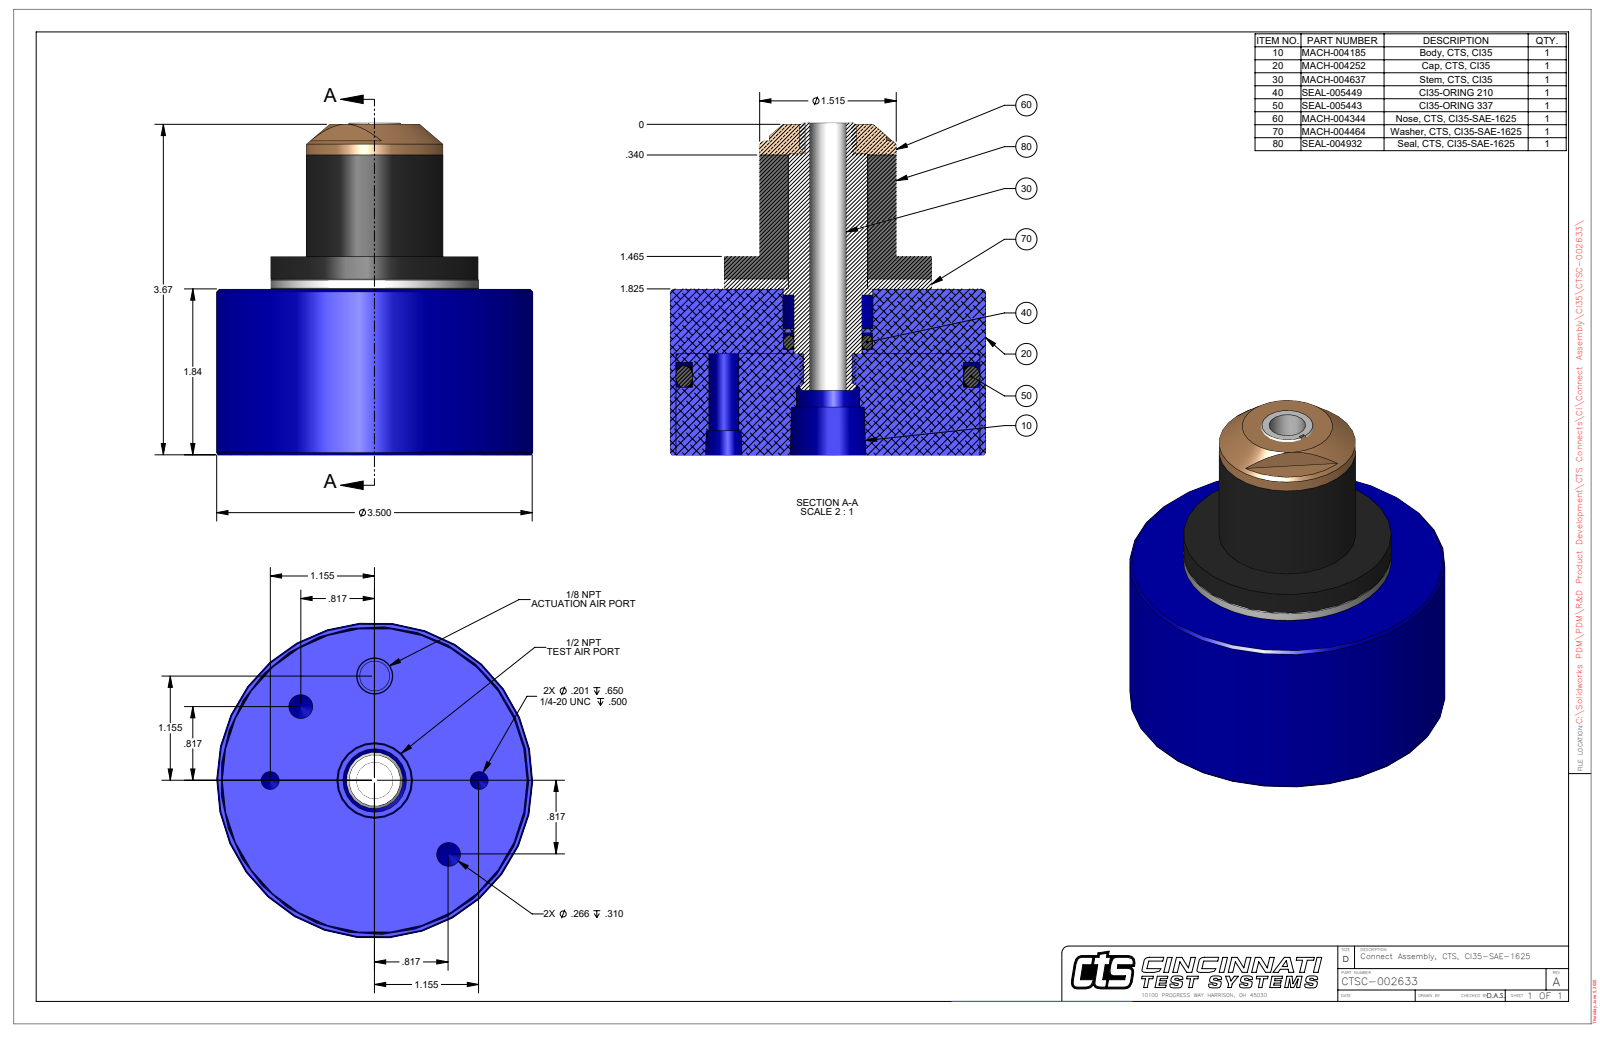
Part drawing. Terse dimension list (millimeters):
name: CTSC-002633
written by: SolidWorks 2023 (AUTOMOTIVE_DESIGN)
unit: mm
bodies: 1 solid, 74 faces (20 planar, 27 cylindrical, 27 other)
size: 93.5 × 88.9 × 88.9
volume: 340 400 mm³; area: 45 740 mm²
holes: 2× ⌀5.1, 2× ⌀6.8, 1× ⌀8.4, 1× ⌀10.3, 1× ⌀17.9, 1× ⌀85.7
bosses: 1× ⌀88.9, 1× ⌀85.5, 1× ⌀58.4, 1× ⌀38.5
rounds: 1× R6.8
face distances: 46.7, 55.9, 9.1, 93.1, 46.4, 37.2, 18.3, 28.5, 37.6, 74.8
hole spacings: 22.5, 29.3, 54.2, 29.3, 41.5, 58.6, 58.7
